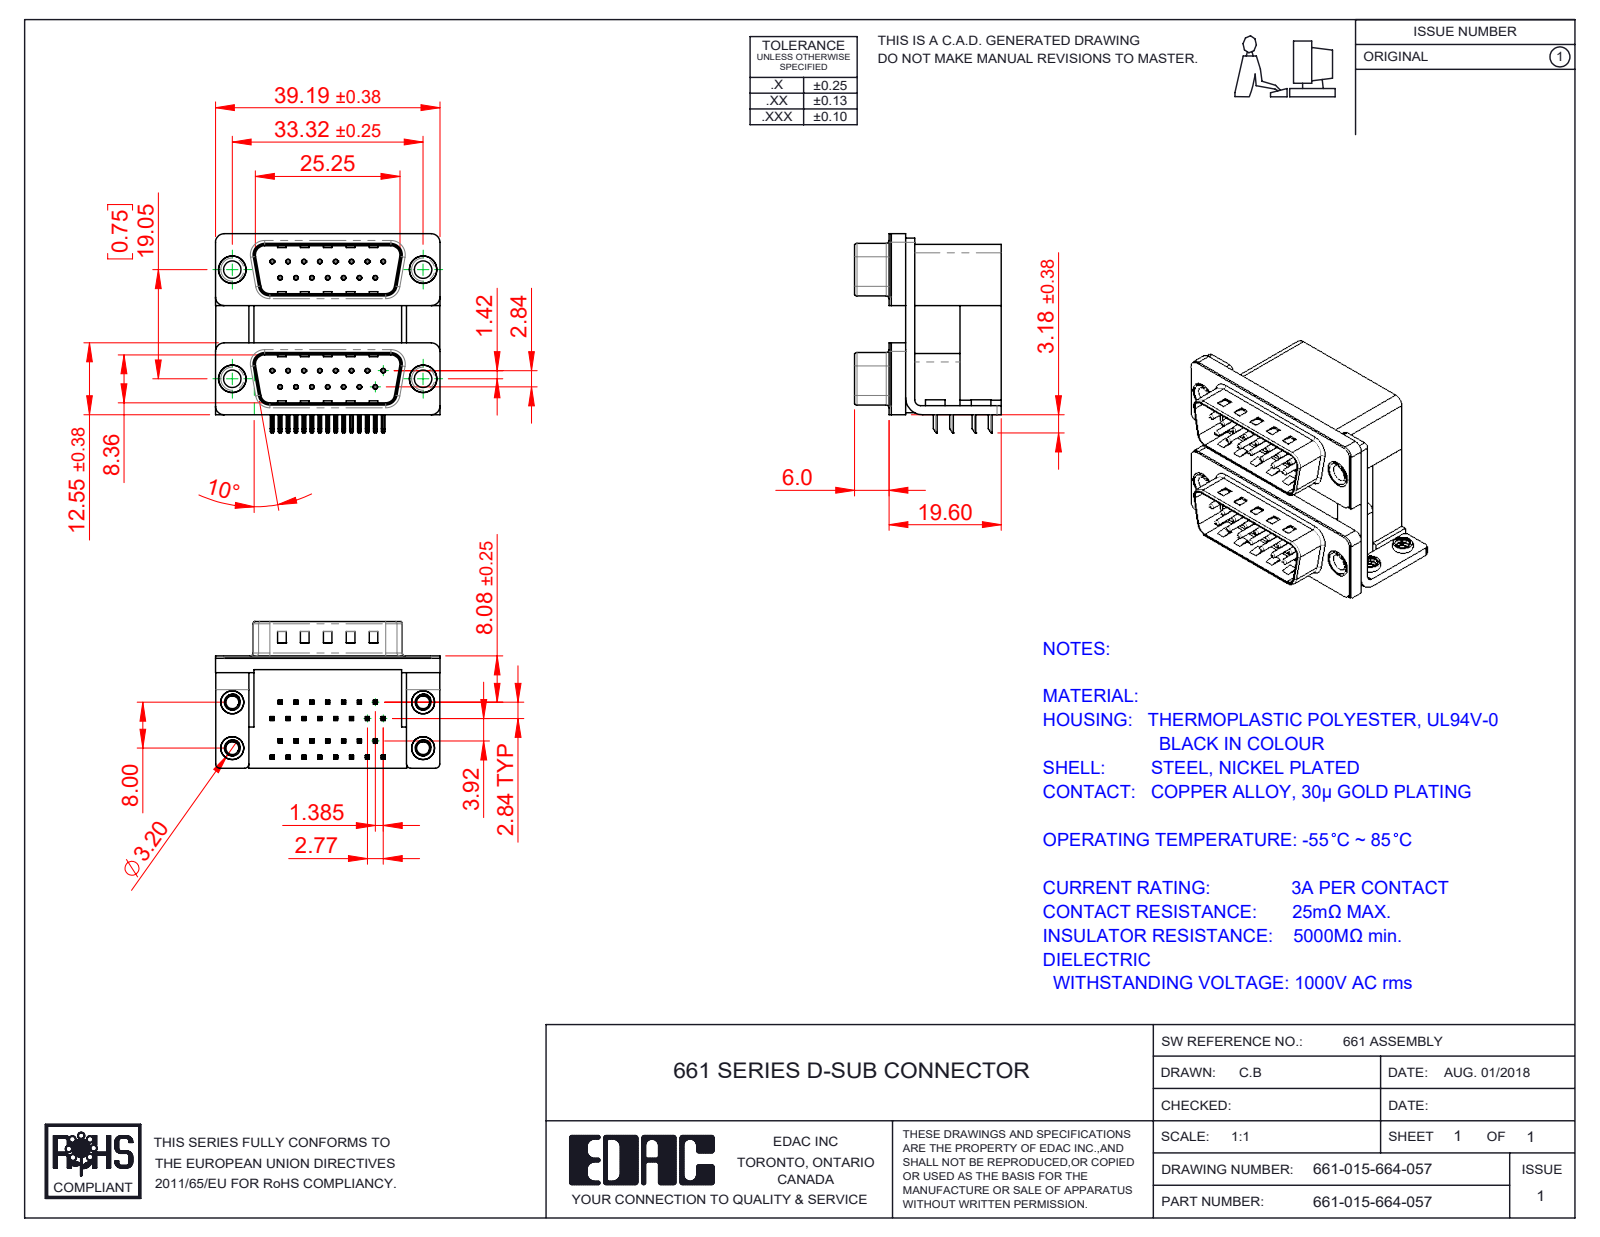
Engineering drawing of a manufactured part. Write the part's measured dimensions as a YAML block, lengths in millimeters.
part_name: "661 Contact Top Lower; 661 4-40 Threaded Board Mount; 661 Housing Lower_15 Contacts; 661 Housing Upper_15 Contacts M (+8 more)"
step_written_by: "SolidWorks 2020 (CONFIG_CONTROL_DESIGN)"
units: millimeters
bodies: {solids: 45, faces: 3018, planar: 1846, cylindrical: 894, other: 278}
overall_size: [39.19, 34.78, 25.6]
volume: 14400
surface_area: 15865
round_holes:
  - {diameter: 0.35, count: 30}
  - {diameter: 0.8, count: 30}
  - {diameter: 2.26, count: 4}
  - {diameter: 2.75, count: 4}
  - {diameter: 3.05, count: 4}
  - {diameter: 3.2, count: 4}
  - {diameter: 3.5, count: 4}
  - {diameter: 4, count: 4}
  - {diameter: 4.8, count: 4}
  - {diameter: 5, count: 4}
round_bosses_or_shafts:
  - {diameter: 0.75, count: 30}
  - {diameter: 4.9, count: 4}
  - {diameter: 4.75, count: 4}
  - {diameter: 4, count: 4}
  - {diameter: 3.85, count: 4}
  - {diameter: 3.4, count: 4}
partial_cylinders:
  - {radius: 0.25, count: 120}
  - {radius: 0.12, count: 60}
  - {radius: 0.5, count: 16}
  - {radius: 1.5, count: 16}
  - {radius: 0.75, count: 8}
  - {radius: 0.9, count: 8}
  - {radius: 1.6, count: 8}
  - {radius: 2, count: 8}
face_to_face_distances: [0.4, 19.05, 19.2, 10.69, 16.7, 2.5, 7.2, 12, 9.5, 18.7]
hole_center_spacings: [3.16, 2.77, 19.25, 5.54, 19.84, 8.31, 20.78, 19.05]
